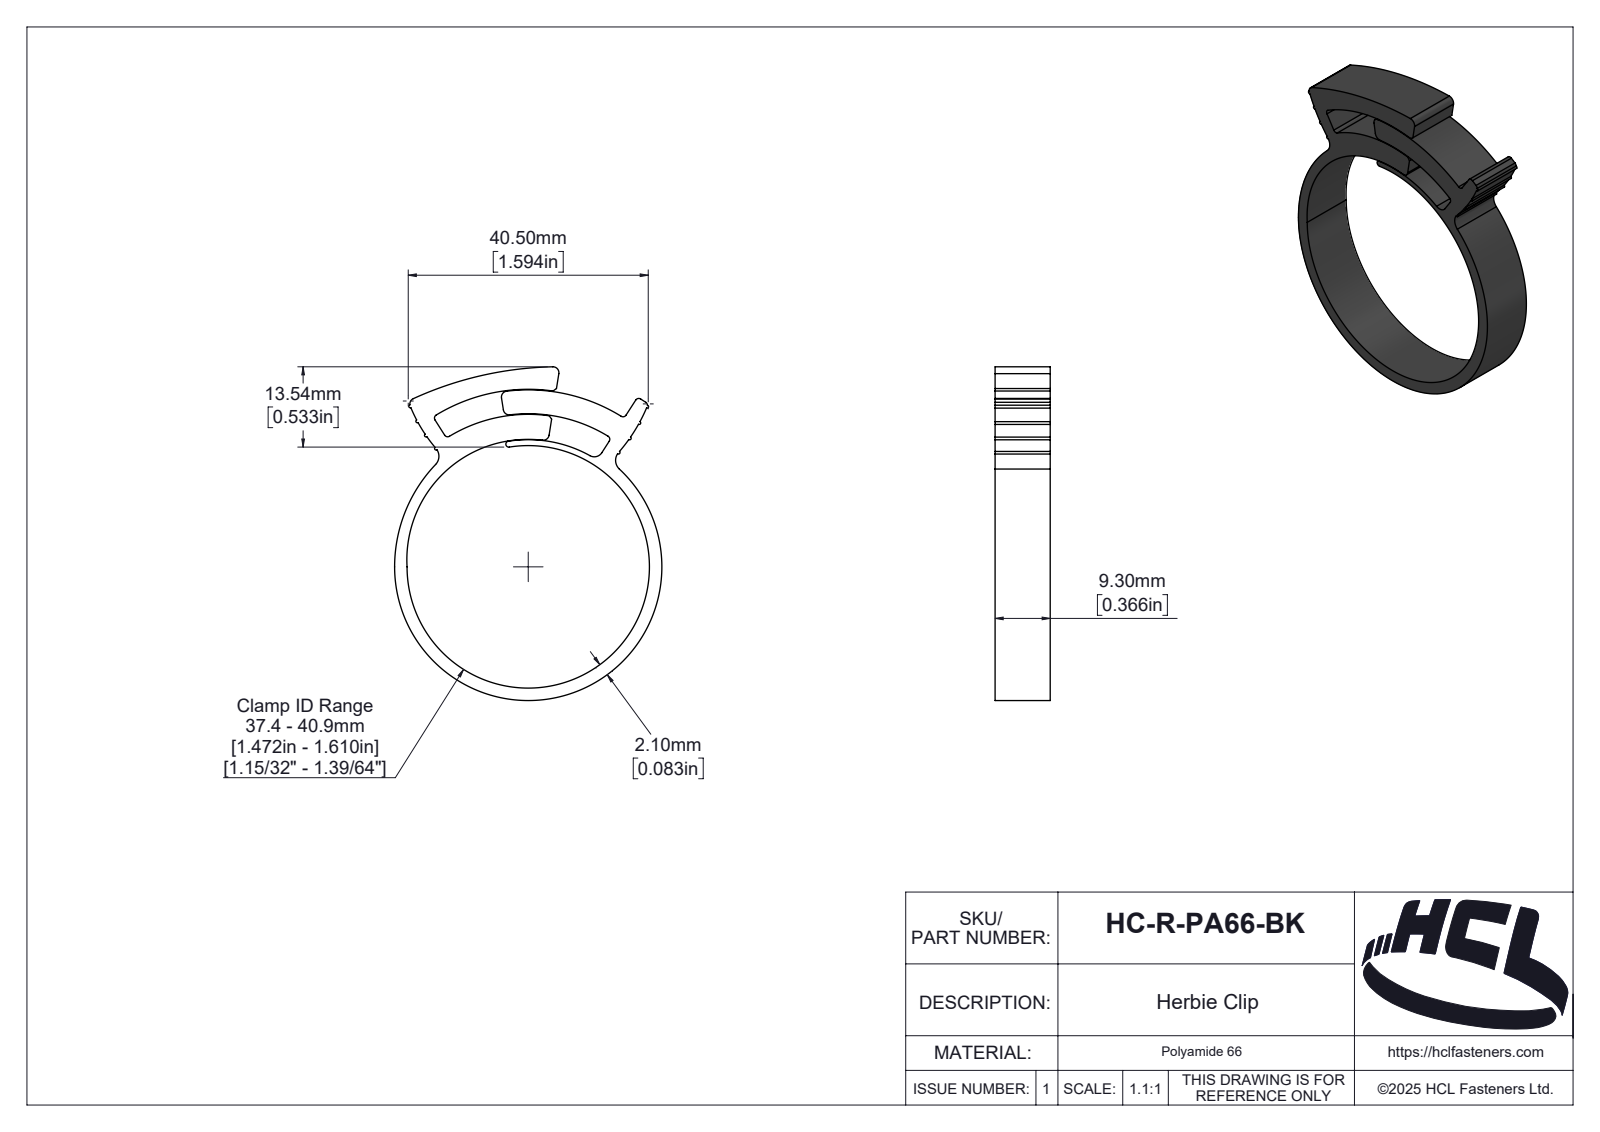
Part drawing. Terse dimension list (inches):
name: HC-R-PA66-BK
written by: SolidWorks 2025 (AUTOMOTIVE_DESIGN)
unit: in
bodies: 1 solid, 162 faces (13 planar, 100 cylindrical, 49 other)
size: 2.216 × 1.776 × 0.366
volume: 0.306 in³; area: 7.716 in²
rounds: 8× R0.01, 6× R0.024, 5× R0.039, 2× R0.079, 1× R0.007, 1× R0.02, 1× R0.026, 1× R0.033
face distances: 0.366
